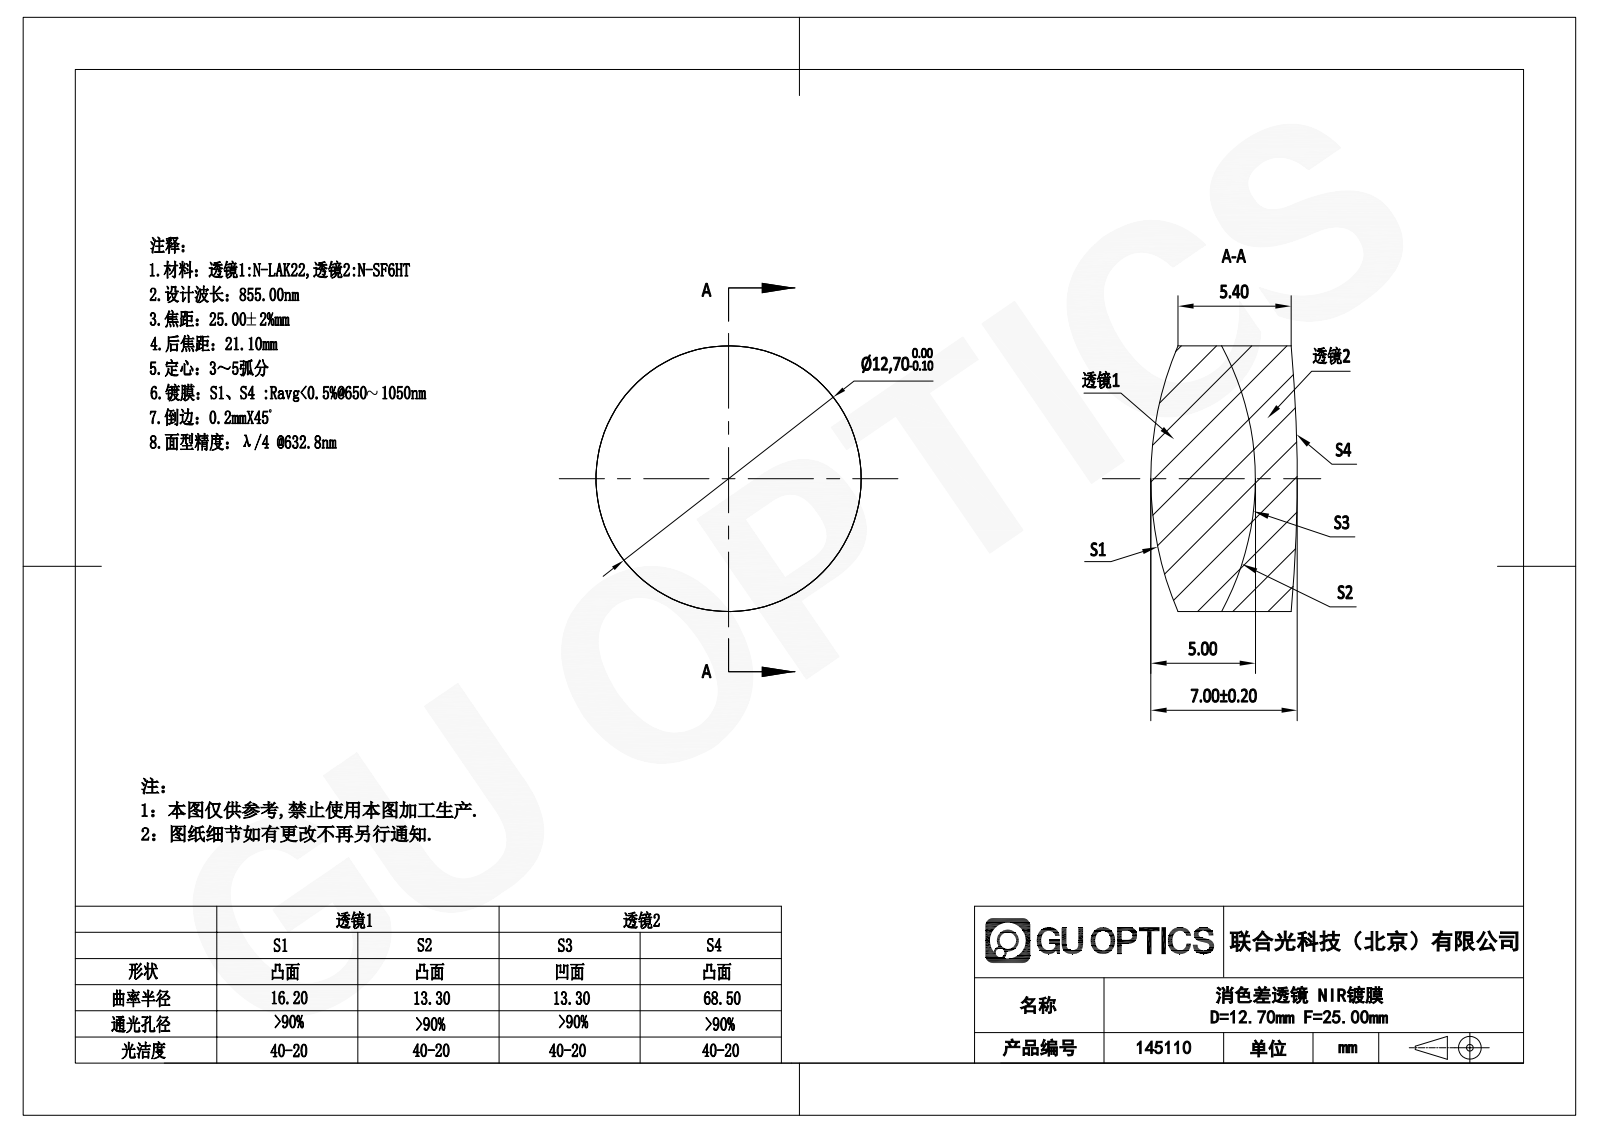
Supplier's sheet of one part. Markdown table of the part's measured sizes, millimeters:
| quantity | value |
| --- | --- |
| part name | 145110 |
| STEP written by | SolidWorks 2016 (AUTOMOTIVE_DESIGN) |
| units | millimeters |
| bodies | 2 solids, 12 faces (0 planar, 4 cylindrical, 8 other) |
| overall size | 12.7 × 12.7 × 7 |
| volume | 787 mm³ |
| surface area | 744 mm² |
| round bosses / shafts (diameter × count) | 12.7 × 1 |
